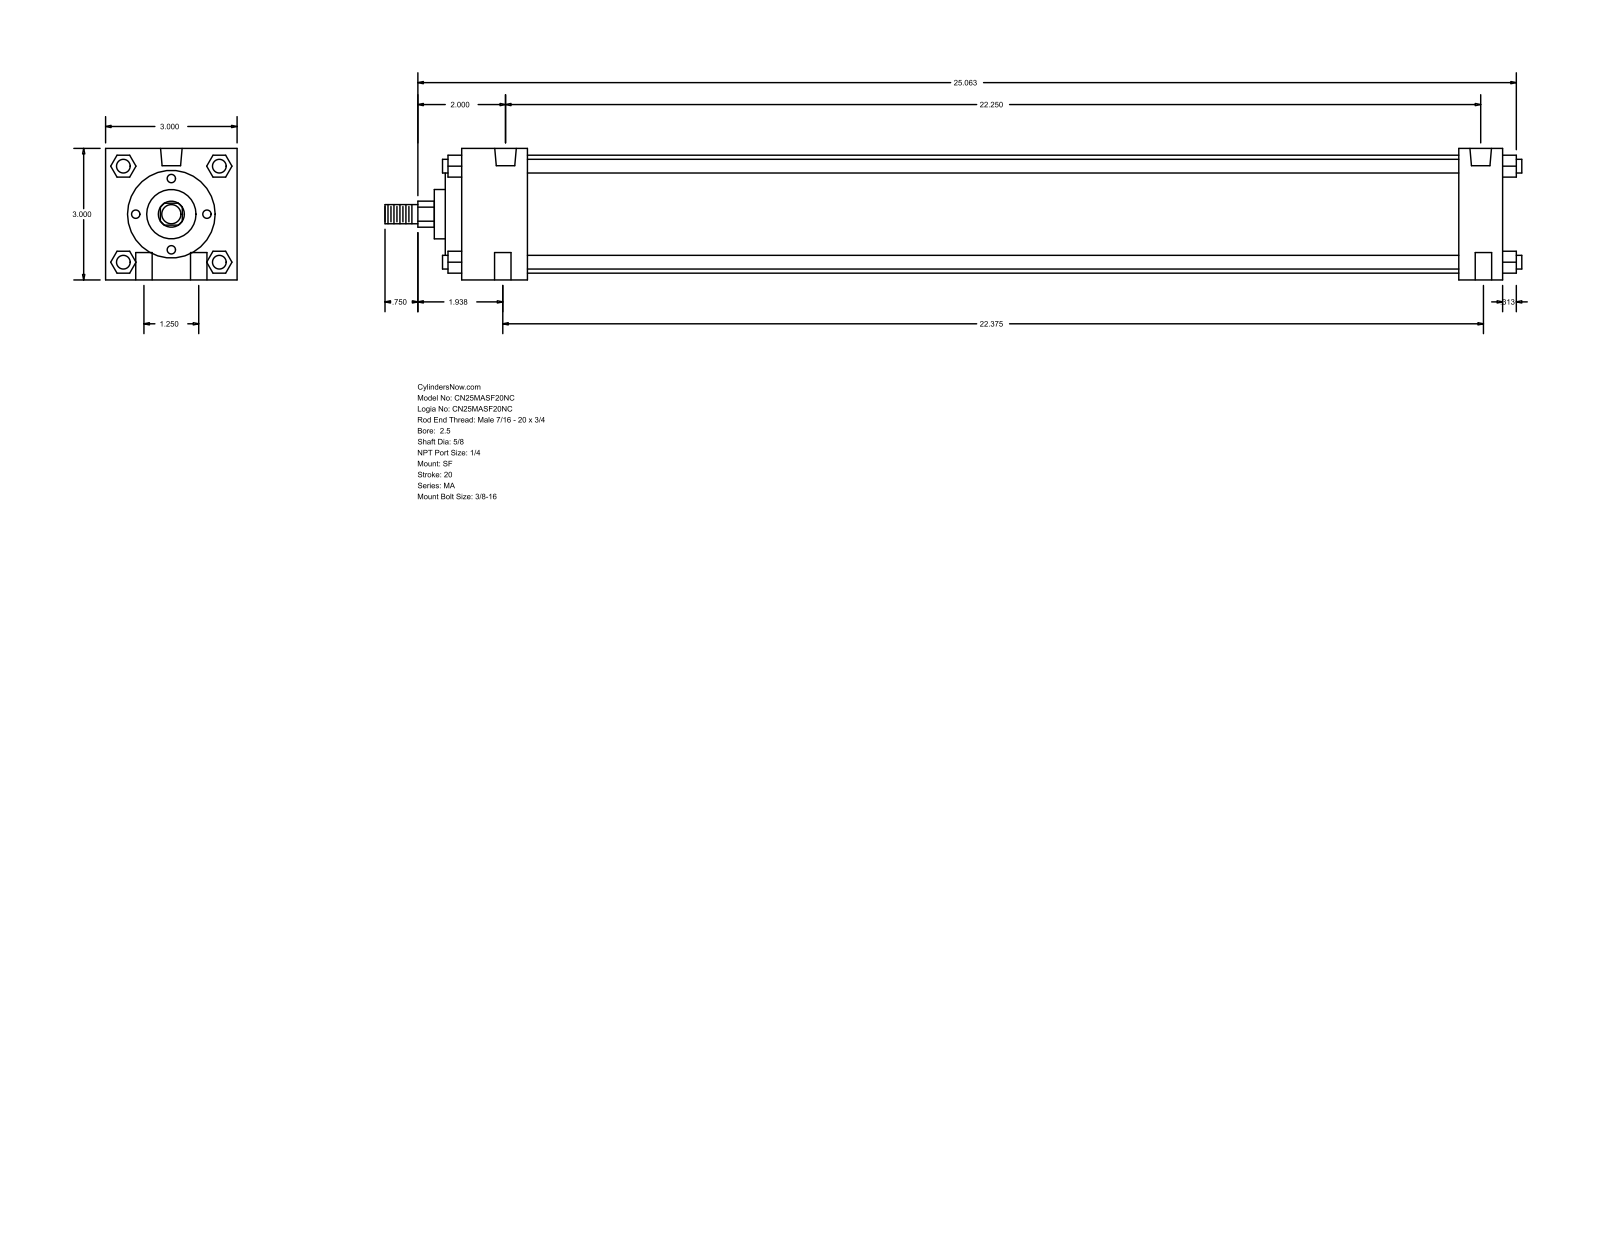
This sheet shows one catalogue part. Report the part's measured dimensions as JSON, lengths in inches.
{"part_name": "MA_SF__0250_0.625", "step_written_by": "GSSL Pune (CONFIG_CONTROL_DESIGN)", "units": "inches", "bodies": {"solids": 0, "faces": 126, "planar": 95, "cylindrical": 31, "other": 0}, "overall_size": [25.937, 3, 3], "round_holes": [[0.375, 4], [0.313, 2], [0.492, 2]], "round_bosses_or_shafts": [[0.313, 4], [2.69, 1], [2, 1], [1.125, 1], [0.625, 1], [0.437, 1]], "partial_cylinders_radius": [[0.297, 1]], "face_to_face_distances": [3, 23.75, 1, 22.75, 1.5, 21.25, 22.25, 0.5, 0.375, 1.875], "hole_center_spacings": [0.628, 22.321, 1.25, 22.25, 22.375, 22.41]}
